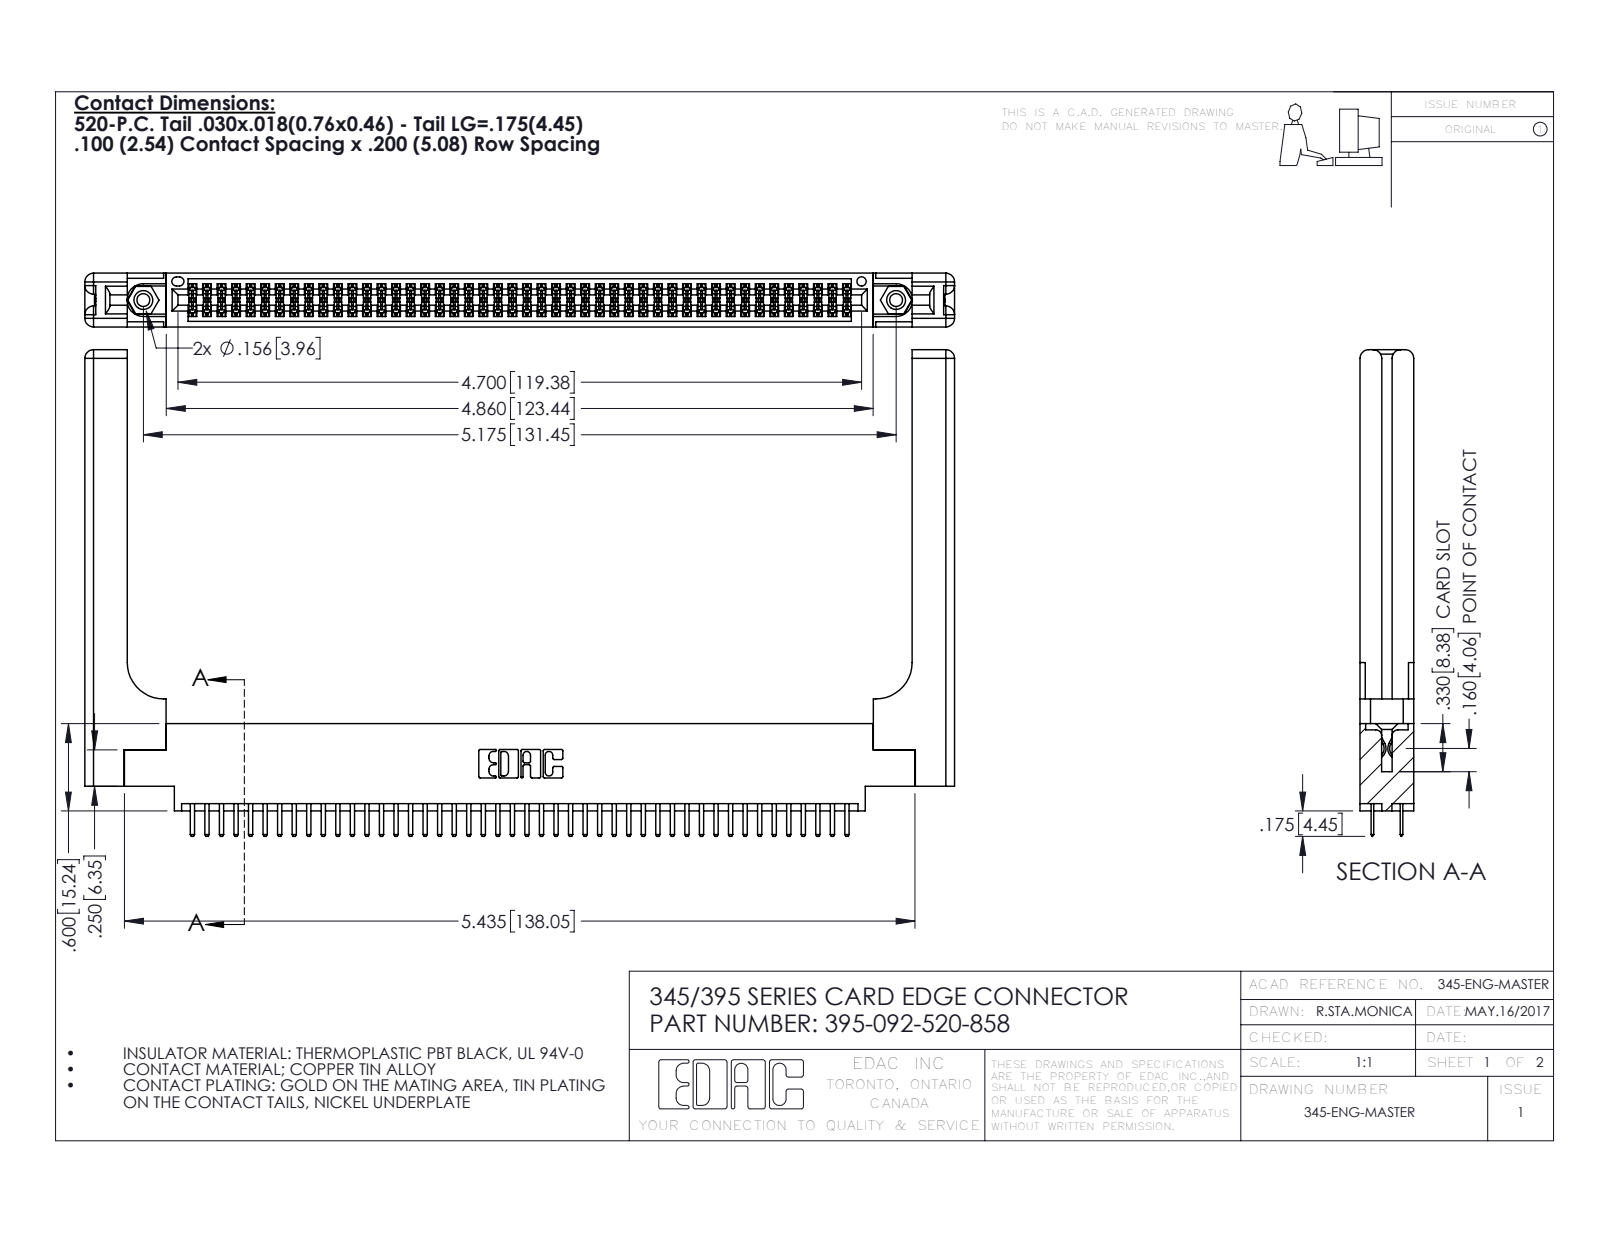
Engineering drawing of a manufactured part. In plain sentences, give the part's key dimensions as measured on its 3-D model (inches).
The part is named "345-292-001_345-293-120; 345 Part_0.170 Offset - 0.156 Dia-TH; 395-092-520-858; 345-250-001_345-250-001-102 (+1 more)". Its 3-D file was written by "SolidWorks 2016 (CONFIG_CONTROL_DESIGN)". It is 97 solids with 5354 faces: 3452 planar, 1842 cylindrical and 60 other. Overall it measures 5.979 by 3.345 by 0.37 inches. Its volume is 1.41 cubic inches and its surface area 41.58 square inches. Round holes: 2 of diameter 0.089, 2 of diameter 0.125, 2 of diameter 0.156, 1 of diameter 0.064. Round bosses or shafts: 2 of diameter 0.155. Partial cylindrical surfaces (rounded edges, fillets, slot ends): 139 of radius 0.006, 96 of radius 0.01, 22 of radius 0.01, 16 of radius 0.06, 6 of radius 0.007, 6 of radius 0.031, 3 of radius 0.026, 2 of radius 0.014. The main face-to-face distances are 0.37, 0.072, 0.298, 0.2, 0.098, 0.272, 0.025, 0.225, 0.148, 0.15. The hole center spacings are 0.27, 4.939, 5.175.
